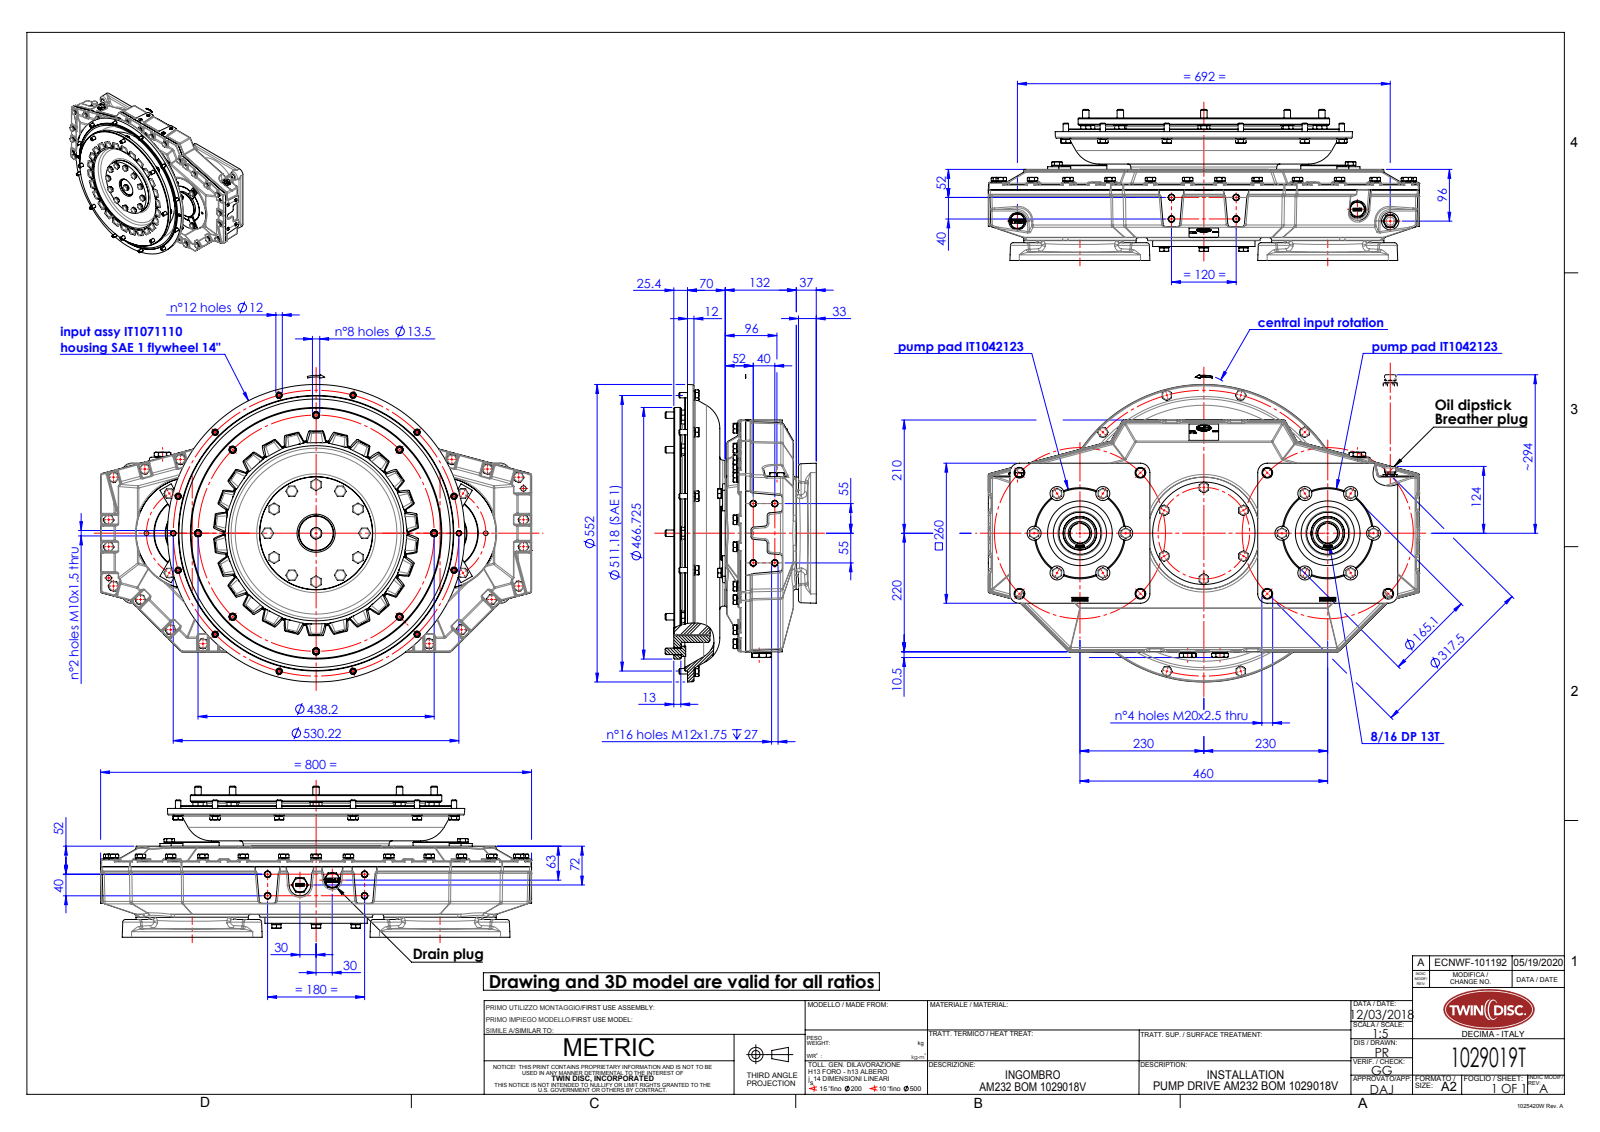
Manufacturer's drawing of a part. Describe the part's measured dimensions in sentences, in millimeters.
The part is named "IT0000203_rev00-installation; 1029019T; ITB00810000_rev01-installation; ITam230-001_rev01-installation (+6 more)". Its 3-D file was written by "SolidWorks 2019 (AUTOMOTIVE_DESIGN)". It is 32 solids with 9009 faces: 3654 planar, 2598 cylindrical and 2757 other. Overall it measures 800 by 570.54 by 280.4 millimeters. Its volume is 13 390 000 cubic millimeters and its surface area 4 296 000 square millimeters. Round holes: 70 of diameter 10.2, 32 of diameter 8.5, 29 of diameter 10.5, 28 of diameter 13, 24 of diameter 12, 18 of diameter 11, 12 of diameter 10, 12 of diameter 26, 8 of diameter 13.5, 8 of diameter 17.5, 7 of diameter 12.2, 3 of diameter 18.5. Round bosses or shafts: 59 of diameter 16.2, 59 of diameter 10, 51 of diameter 18.1, 27 of diameter 18, 27 of diameter 12, 20 of diameter 24, 9 of diameter 20, 7 of diameter 21.1. Partial cylindrical surfaces (rounded edges, fillets, slot ends): 336 of radius 2, 180 of radius 2.5, 142 of radius 5, 132 of radius 3, 116 of radius 1.5, 58 of radius 0.45, 53 of radius 60, 12 of radius 10.97. The main face-to-face distances are 38, 10, 48, 20, 58, 152, 94, 132, 126.5, 85.4. The hole center spacings are 120, 57.4, 75, 138.58, 40, 150, 207.84, 30.
